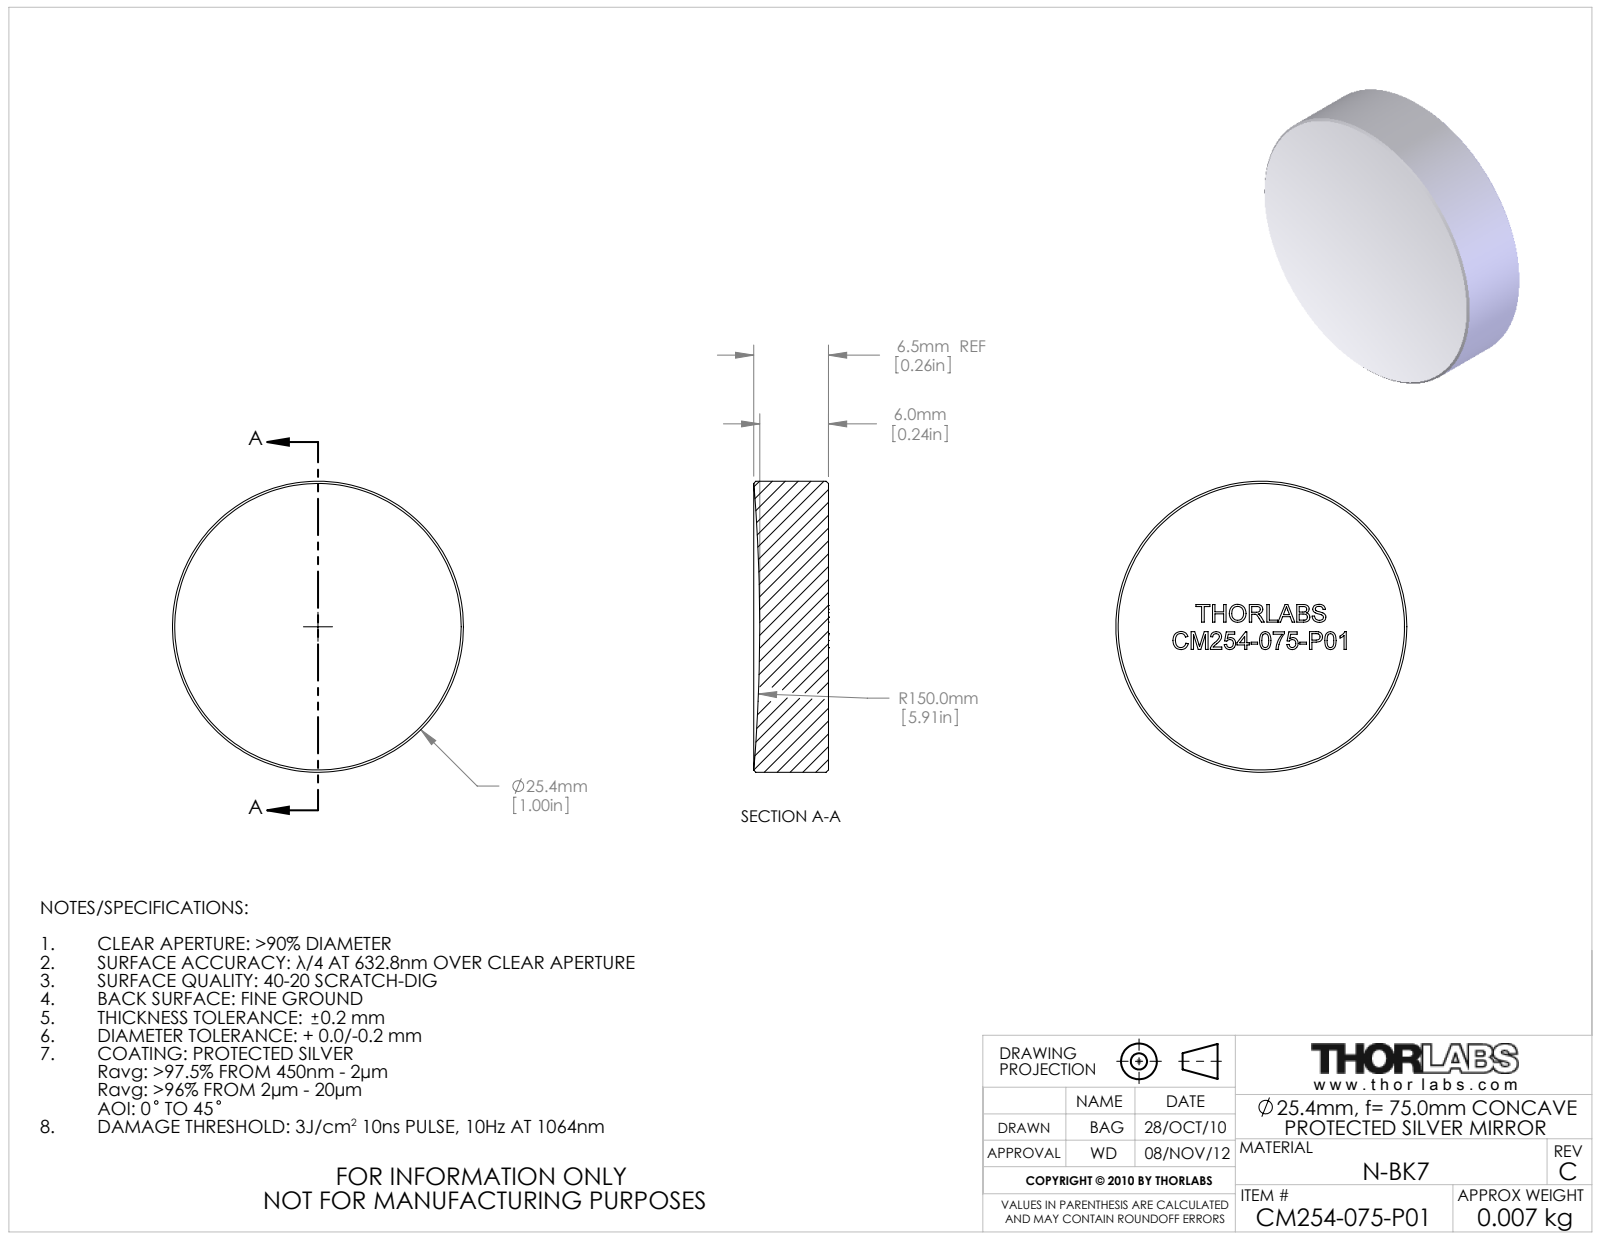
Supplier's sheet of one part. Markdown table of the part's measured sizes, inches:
| quantity | value |
| --- | --- |
| part name | 17569-E0W |
| STEP written by | SolidWorks 2009 (AUTOMOTIVE_DESIGN) |
| units | inches |
| bodies | 1 solid, 281 faces (163 planar, 2 cylindrical, 116 other) |
| overall size | 1 × 1 × 0.257 |
| volume | 0.194 in³ |
| surface area | 2.35 in² |
| round bosses / shafts (diameter × count) | 1 × 1 |
| main face-to-face distances | 0.061, 0.076, 0.094, 0.054, 0.052, 0.037, 0.093, 0.163, 0.211, 0.029 |
